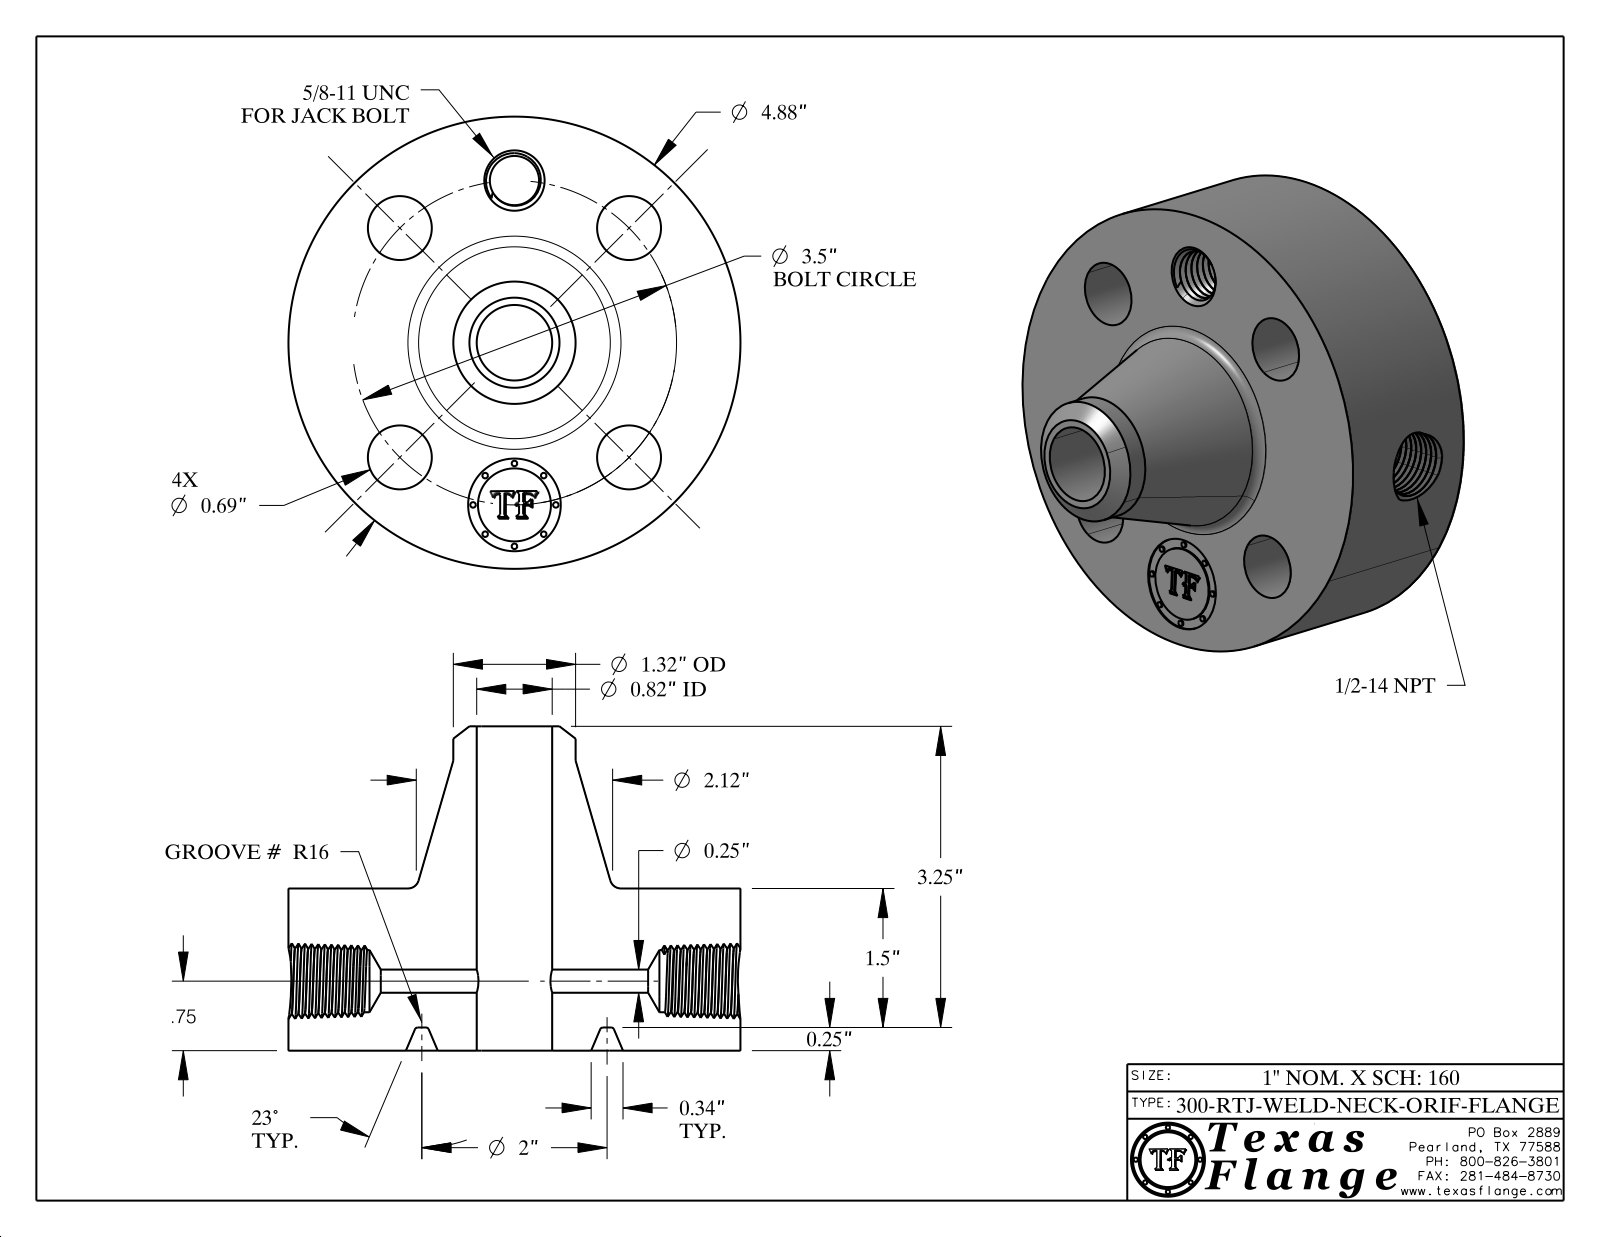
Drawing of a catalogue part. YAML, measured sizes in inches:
part_name: "300-RTJ-WELD-NECK"
step_written_by: "CATIA V5 STEP AP214 (AUTOMOTIVE_DESIGN)"
units: inches
bodies: {solids: 1, faces: 789, planar: 370, cylindrical: 91, other: 328}
overall_size: [4.88, 4.88, 3.5]
volume: 30.31
surface_area: 105.6
round_holes:
  - {diameter: 0.69, count: 4}
  - {diameter: 0.25, count: 1}
  - {diameter: 0.531, count: 1}
  - {diameter: 0.672, count: 1}
  - {diameter: 0.815, count: 1}
  - {diameter: 1, count: 1}
round_bosses_or_shafts:
  - {diameter: 0.061, count: 8}
  - {diameter: 4.88, count: 1}
  - {diameter: 1.32, count: 1}
  - {diameter: 0.788, count: 1}
face_to_face_distances: [1.75, 0.25, 1.5, 1.735, 1.485, 0.015, 3.5, 3.25, 1.765, 0.298]
hole_center_spacings: [1.75, 1.339, 2.475, 3.233, 3.5]
